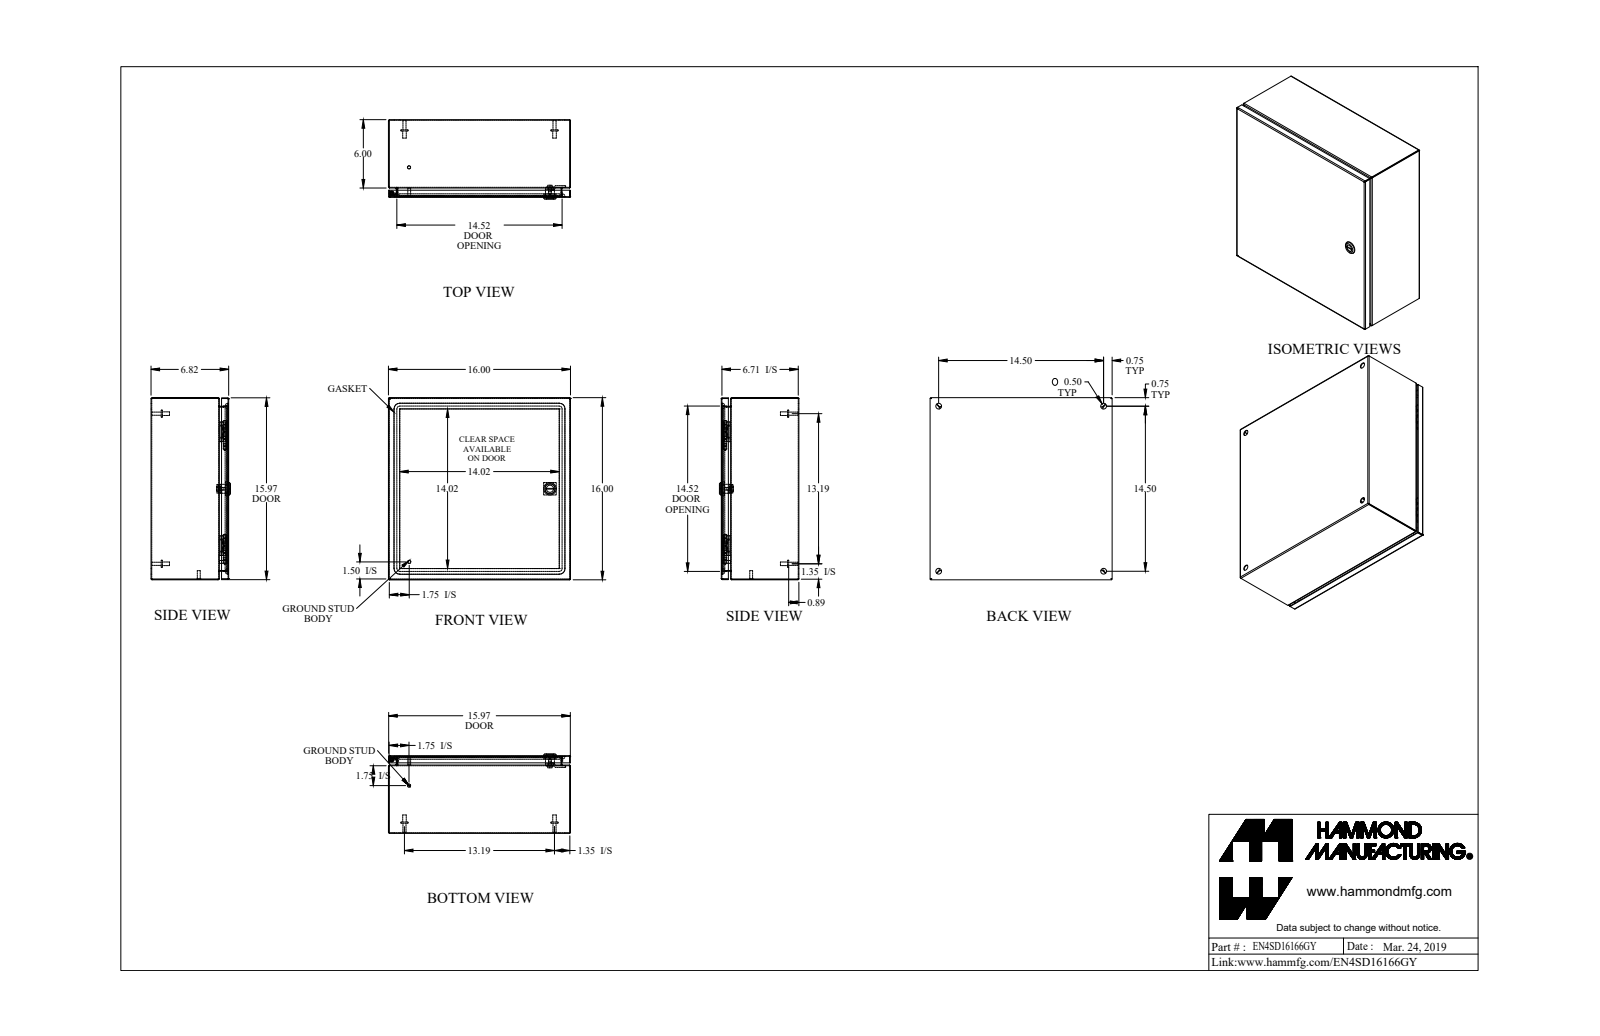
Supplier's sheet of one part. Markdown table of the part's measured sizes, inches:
| quantity | value |
| --- | --- |
| part name | EN4SD16166GY_Default |
| STEP written by | SolidWorks 2019 (CONFIG_CONTROL_DESIGN) |
| units | inches |
| bodies | 21 solids, 634 faces (285 planar, 213 cylindrical, 136 other) |
| overall size | 16 × 16 × 6.982 |
| volume | 64.65 in³ |
| surface area | 2 185 in² |
| round holes (diameter × count) | 0.5 × 4, 0.172 × 1, 0.232 × 1, 0.24 × 1, 0.242 × 1, 0.625 × 1, 0.785 × 1 |
| round bosses / shafts (diameter × count) | 0.625 × 4, 0.313 × 4, 0.27 × 4, 0.281 × 2, 0.25 × 2, 1.1 × 1, 0.525 × 1, 0.455 × 1 |
| partial cylindrical surfaces (radius × count) | 0.029 × 21, 0.086 × 21, 0.25 × 16, 19 × 8, 0.006 × 4, 0.062 × 4, 0.499 × 4, 0.125 × 2 |
| main face-to-face distances | 0.057, 6.765, 15.943, 6.708, 6.822, 15.886, 16, 0.822, 5.943, 0.749 |
| hole center spacings | 14.5, 20.506, 7.326, 7.327, 15.271, 15.272 |
